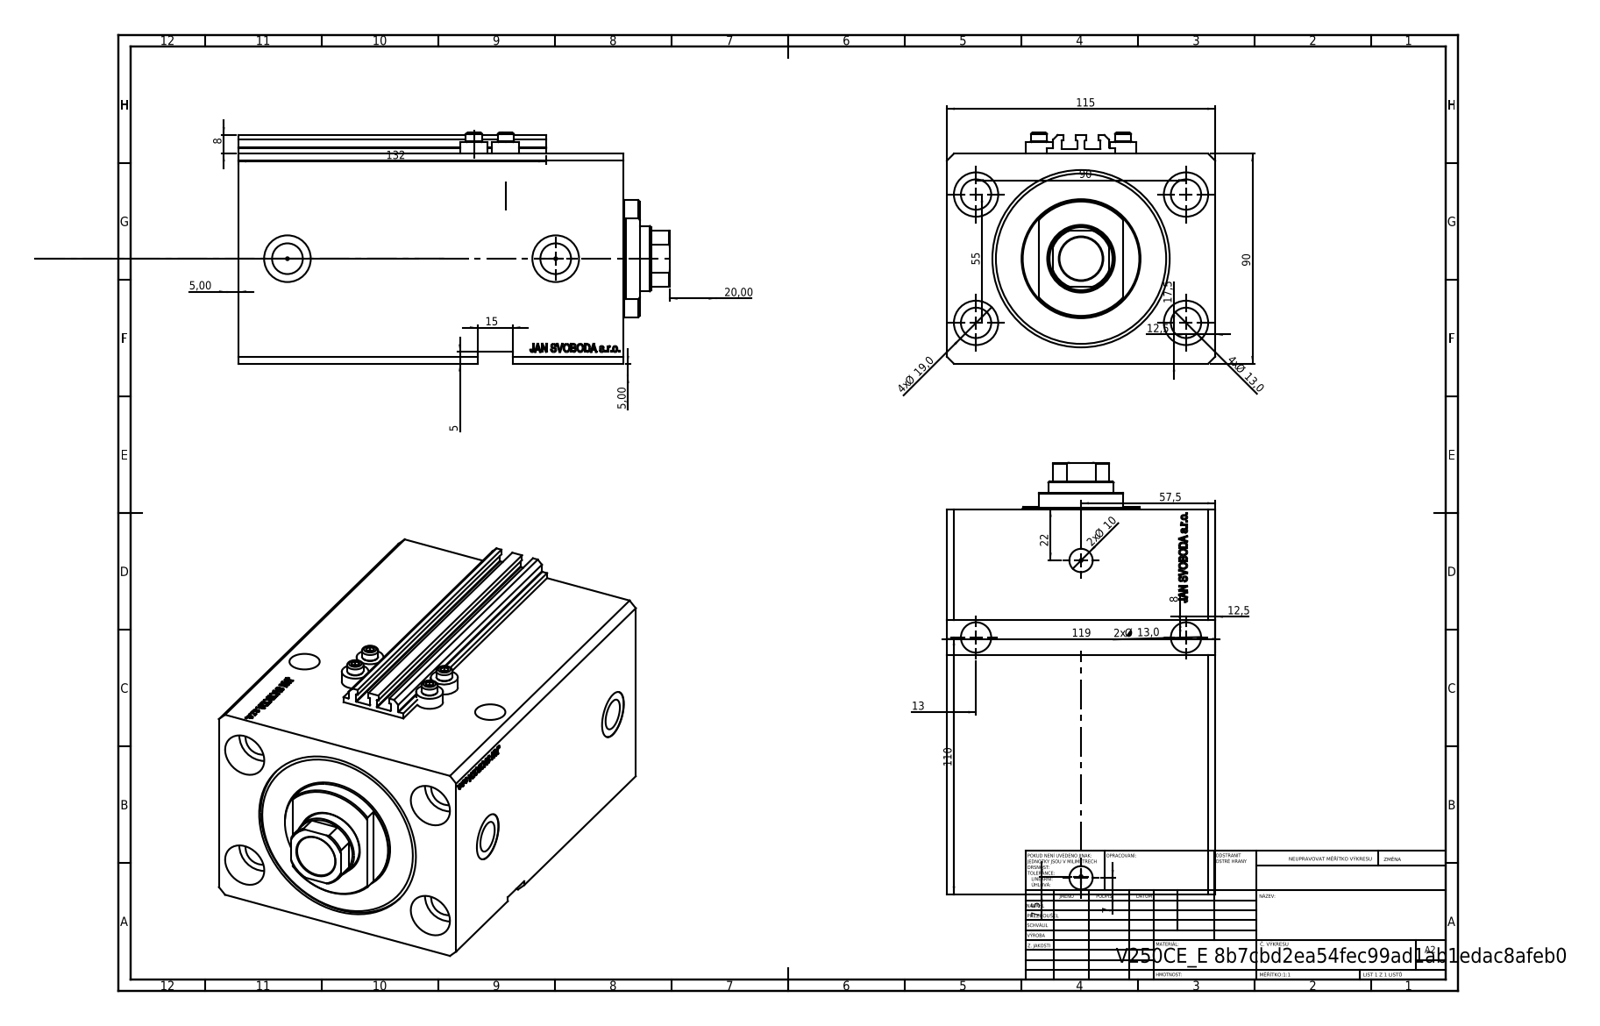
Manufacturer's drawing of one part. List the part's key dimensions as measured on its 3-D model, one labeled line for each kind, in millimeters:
Part name (STEP PRODUCT): V250CE_C_VCP; V250CE_VC_E; ALLEN BOLT V250CE; V250CE_E_Body
STEP written by: SolidWorks 2019 (CONFIG_CONTROL_DESIGN)
Units: millimetres
Bodies: 8 solids, 1123 faces (547 planar, 138 cylindrical, 438 other)
Overall size (bounding box): 184.9 × 115 × 99
Volume: 1 396 000 mm³ · Surface area: 214 831 mm²
Round holes (diameter × count): ⌀13 ×6, ⌀1.25 ×4, ⌀4 ×4, ⌀19 ×4, ⌀10 ×2, ⌀13.16 ×2, ⌀20 ×2, ⌀18.5 ×1, ⌀28 ×1, ⌀63 ×1, ⌀76 ×1
Round bosses / shafts (diameter × count): ⌀11.6 ×4, ⌀7 ×4, ⌀50 ×1
Partial cylindrical surfaces — rounded edges, fillets, slot ends (radius × count): R0.2 ×10, R13.5 ×1
Main face-to-face distances: 90, 115, 165, 17.9, 147.1, 117, 134.9, 30.1, 80, 54.9
Hole centre spacings: 52.74, 90, 13.6, 27.39, 28.46, 33.62, 36, 38.48
